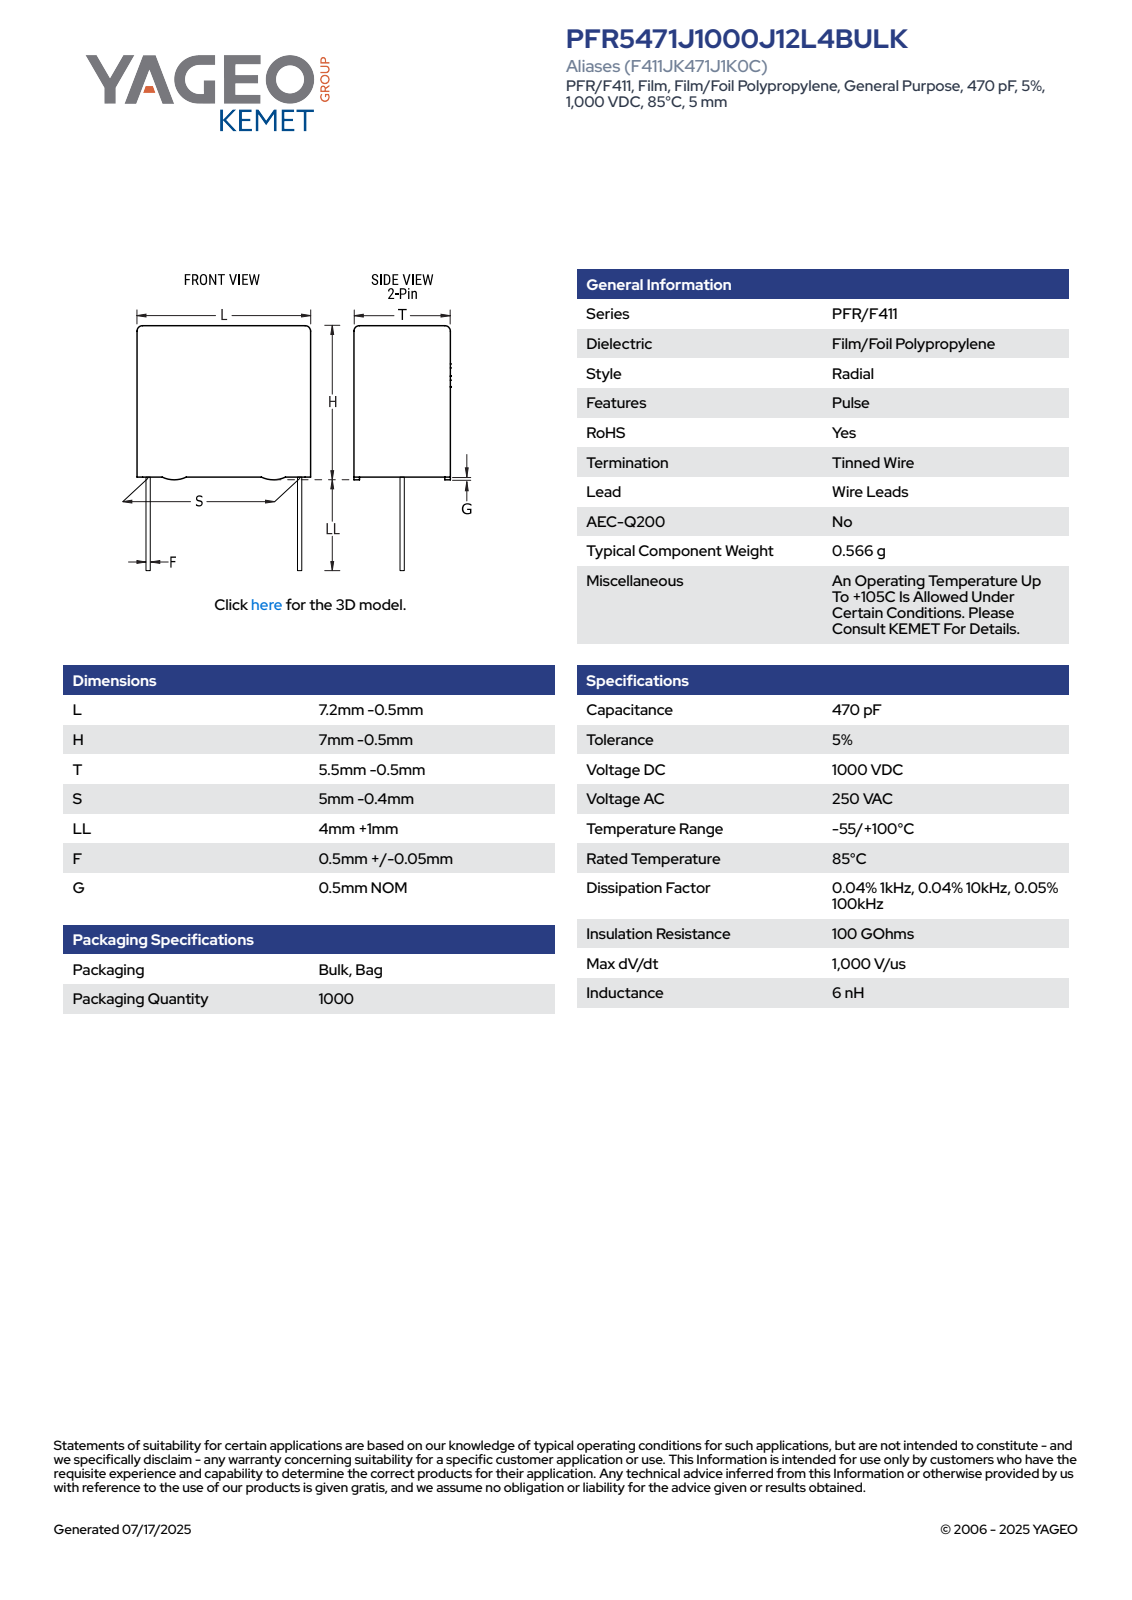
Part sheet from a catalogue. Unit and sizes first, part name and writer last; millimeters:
Units: millimetres
Overall size (bounding box): 11.5 × 6.7 × 5
Round bosses / shafts (diameter × count): ⌀0.55 ×2
Partial cylindrical surfaces — rounded edges, fillets, slot ends (radius × count): R0.5 ×4
Main face-to-face distances: 5, 6.7, 6, 4.72, 4.43, 4.71, 0.5, 6.5, 2.49, 5.5
Volume: 203 mm³ · Surface area: 232 mm²
Bodies: 4 solids, 89 faces (81 planar, 8 cylindrical, 0 other)
Part name (STEP PRODUCT): CFR_RBG_7.2X7X5.5_L6.7H6.5T5S5LL5F0.55G0.5
STEP written by: SolidWorks 2021 (AUTOMOTIVE_DESIGN)
